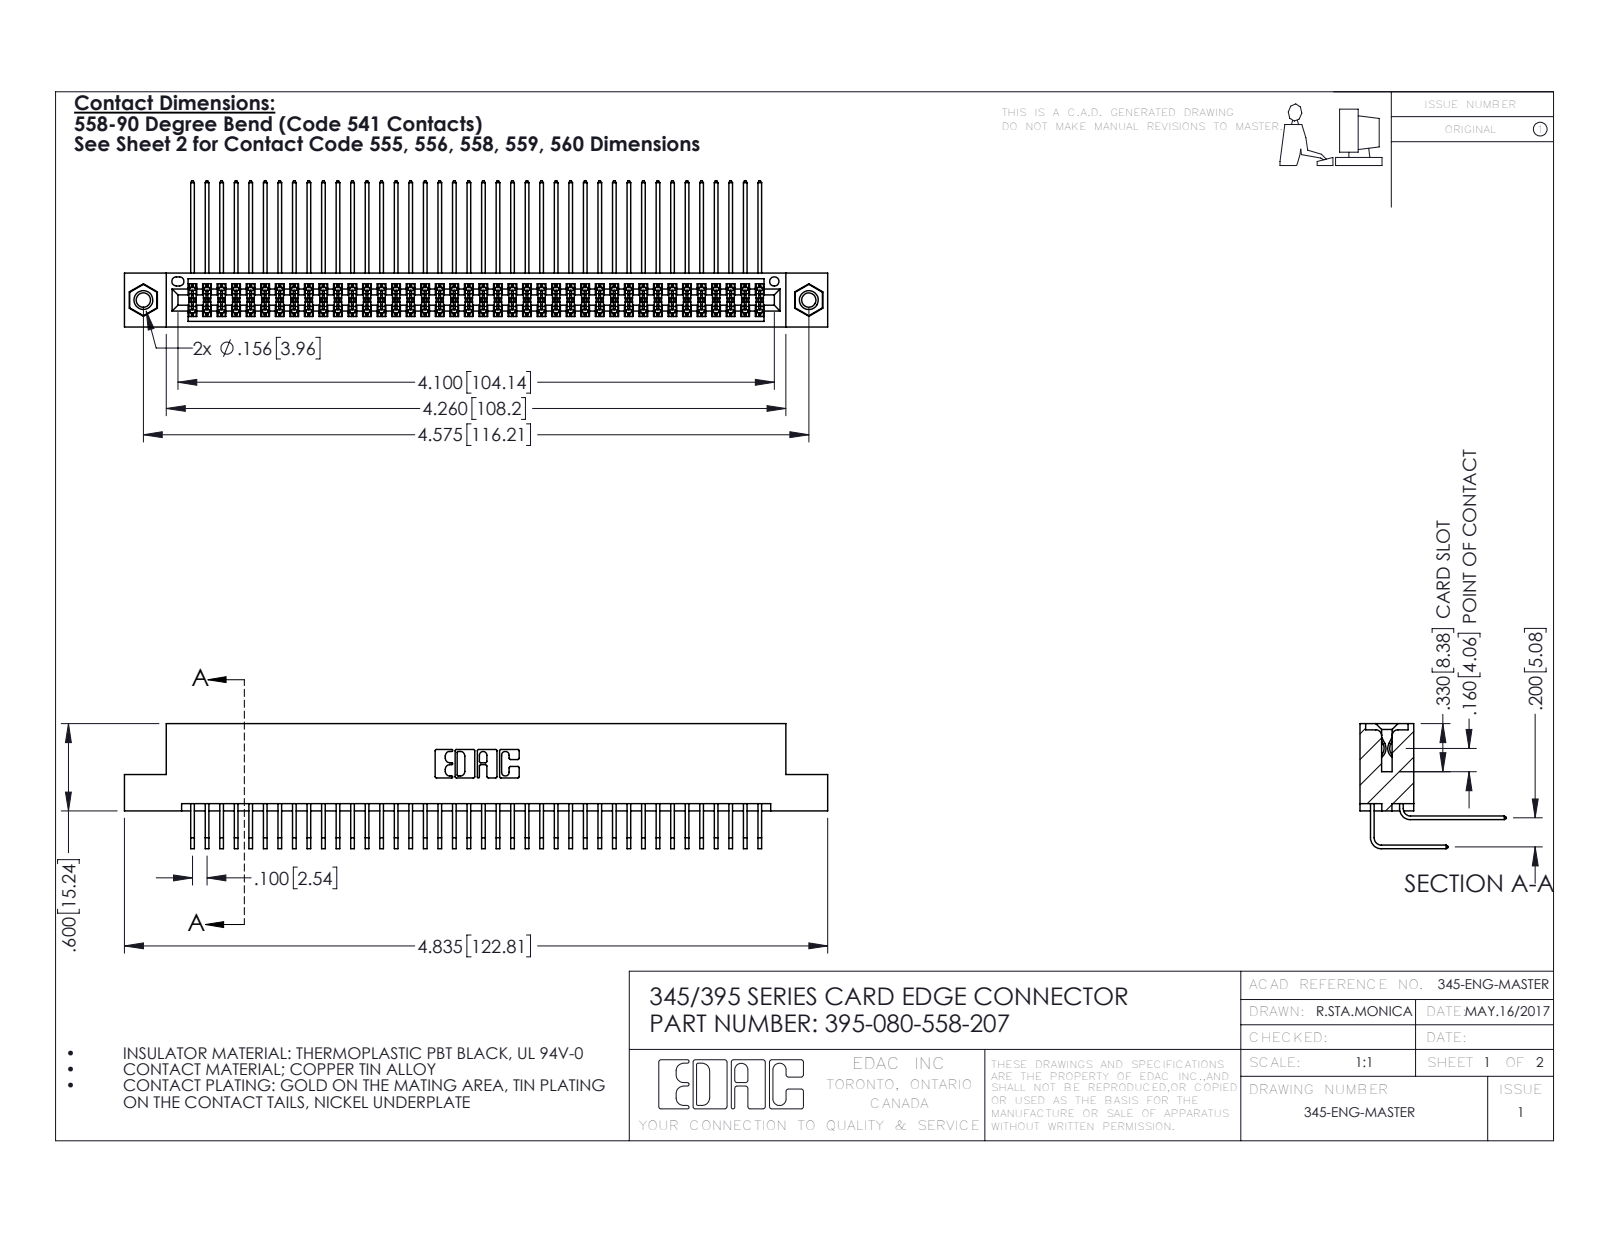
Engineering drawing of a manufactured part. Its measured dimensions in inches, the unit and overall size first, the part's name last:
Units: inches
Overall size (bounding box): 4.835 × 1.005 × 0.859
Round holes (diameter × count): ⌀0.098 ×2, ⌀0.125 ×2, ⌀0.156 ×2, ⌀0.064 ×1
Round bosses / shafts (diameter × count): ⌀0.155 ×2
Partial cylindrical surfaces — rounded edges, fillets, slot ends (radius × count): R0.006 ×121, R0.01 ×22, R0.007 ×6, R0.031 ×6, R0.026 ×3, R0.014 ×2, R0.019 ×2, R0.022 ×2
Main face-to-face distances: 0.072, 0.298, 0.2, 0.37, 0.098, 0.272, 0.025, 0.225, 0.025, 0.175
Hole centre spacings: 0.27, 4.339, 4.575
Volume: 0.754 in³ · Surface area: 31.66 in²
Bodies: 83 solids, 4346 faces (2912 planar, 1418 cylindrical, 16 other)
Part name (STEP PRODUCT): 345-250-001_345-250-005-103; 345-292-001_558 Tail - 2; 395-080-558-207; 345 Part_Flush Mounting Lugs - 0.156 Dia-TI (+1 more)
STEP written by: SolidWorks 2016 (CONFIG_CONTROL_DESIGN)
